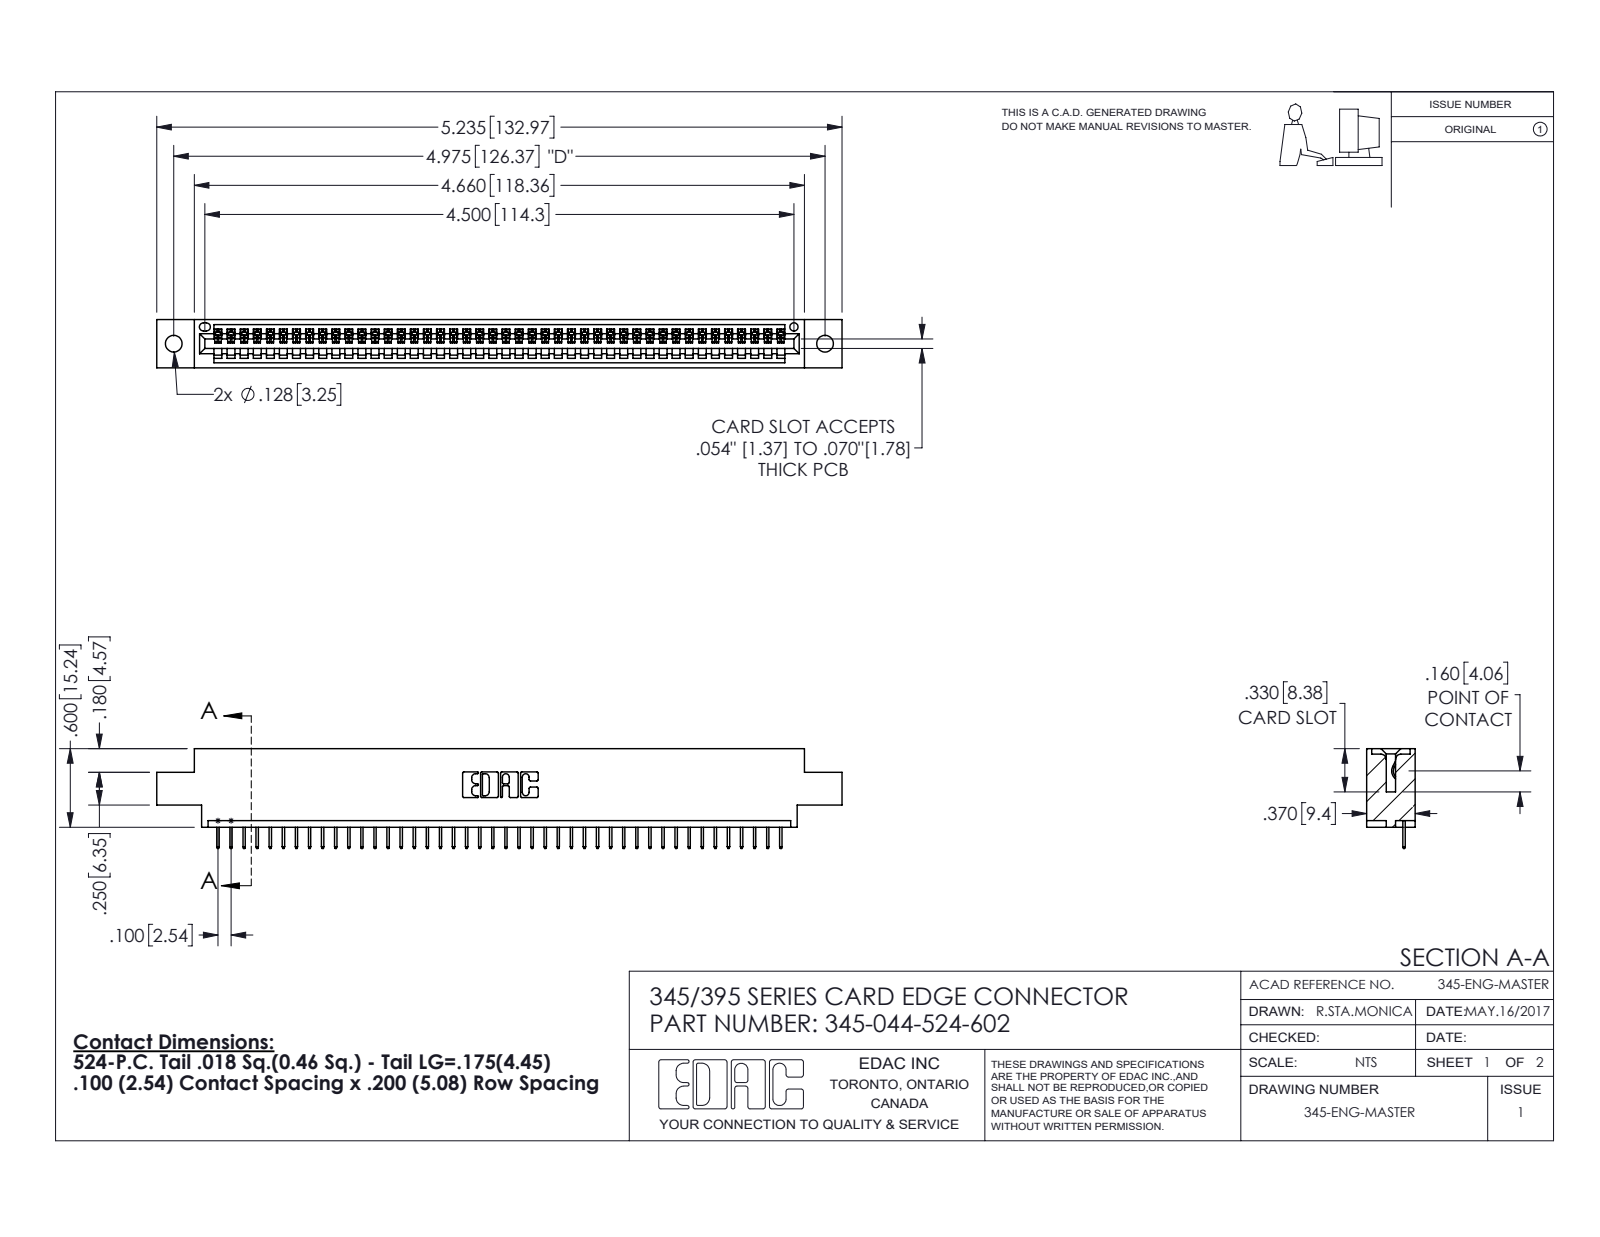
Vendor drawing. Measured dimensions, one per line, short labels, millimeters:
name: 345-292-001_345-293-124; 345 Part_0.170 Offset - 0.128 Dia; 345-044-524-602
written by: SolidWorks 2016 (CONFIG_CONTROL_DESIGN)
unit: mm
bodies: 45 solids, 2858 faces (2108 planar, 750 cylindrical, 0 other)
size: 133 × 19.4 × 9.4
volume: 12 300 mm³; area: 15 700 mm²
holes: 2× ⌀3.3, 1× ⌀1.6
rounds: 88× R0.2, 22× R0.3, 6× R0.2, 6× R0.8, 3× R0.7, 2× R0.8, 2× R1, 1× R0.4
face distances: 1.8, 7.6, 9.4, 5.1, 2.5, 6.9, 0.6, 5.7, 1.8, 4.4
hole spacings: 6.9, 120.4, 126.4
